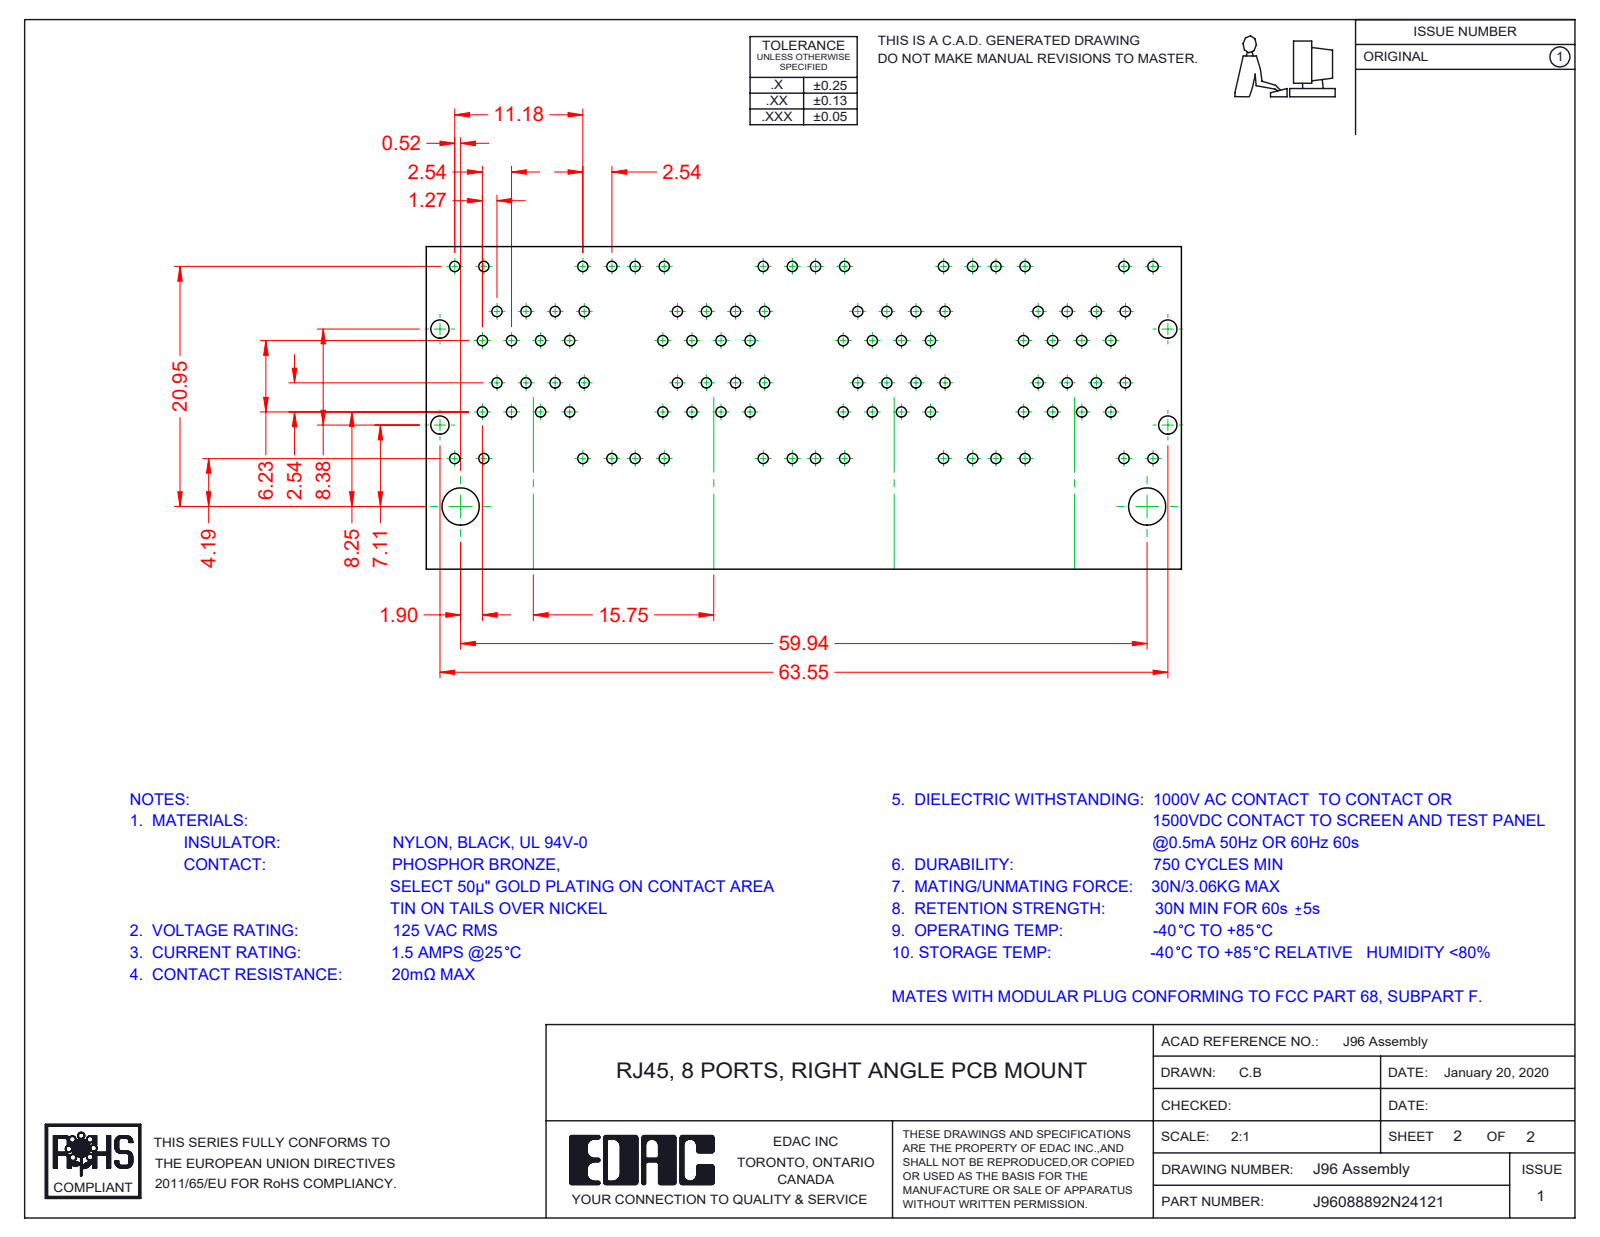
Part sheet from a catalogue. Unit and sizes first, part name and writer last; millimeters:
Units: millimetres
Overall size (bounding box): 64.05 × 29.58 × 28.68
Round holes (diameter × count): ⌀1.7 ×3
Round bosses / shafts (diameter × count): ⌀1.68 ×3
Partial cylindrical surfaces — rounded edges, fillets, slot ends (radius × count): R0.25 ×124, R0.35 ×73, R1 ×72, R0.5 ×49, R0.91 ×32, R0.2 ×21, R0.7 ×11, R0.22 ×8
Main face-to-face distances: 15.75, 0.35, 9.95, 1.17, 1.6, 0.54, 9.98, 10.18, 12.67, 3.37
Hole centre spacings: 15.75, 31.5
Volume: 24 160 mm³ · Surface area: 63 658 mm²
Bodies: 96 solids, 7642 faces (6069 planar, 1307 cylindrical, 266 other)
Part name (STEP PRODUCT): 96 Insulator Insert; 96 LED RH Lower_4-Orange; 96 Contact Lock Upper; 96 LED RH Upper_4-Orange (+8 more)
STEP written by: SolidWorks 2016 (CONFIG_CONTROL_DESIGN)
